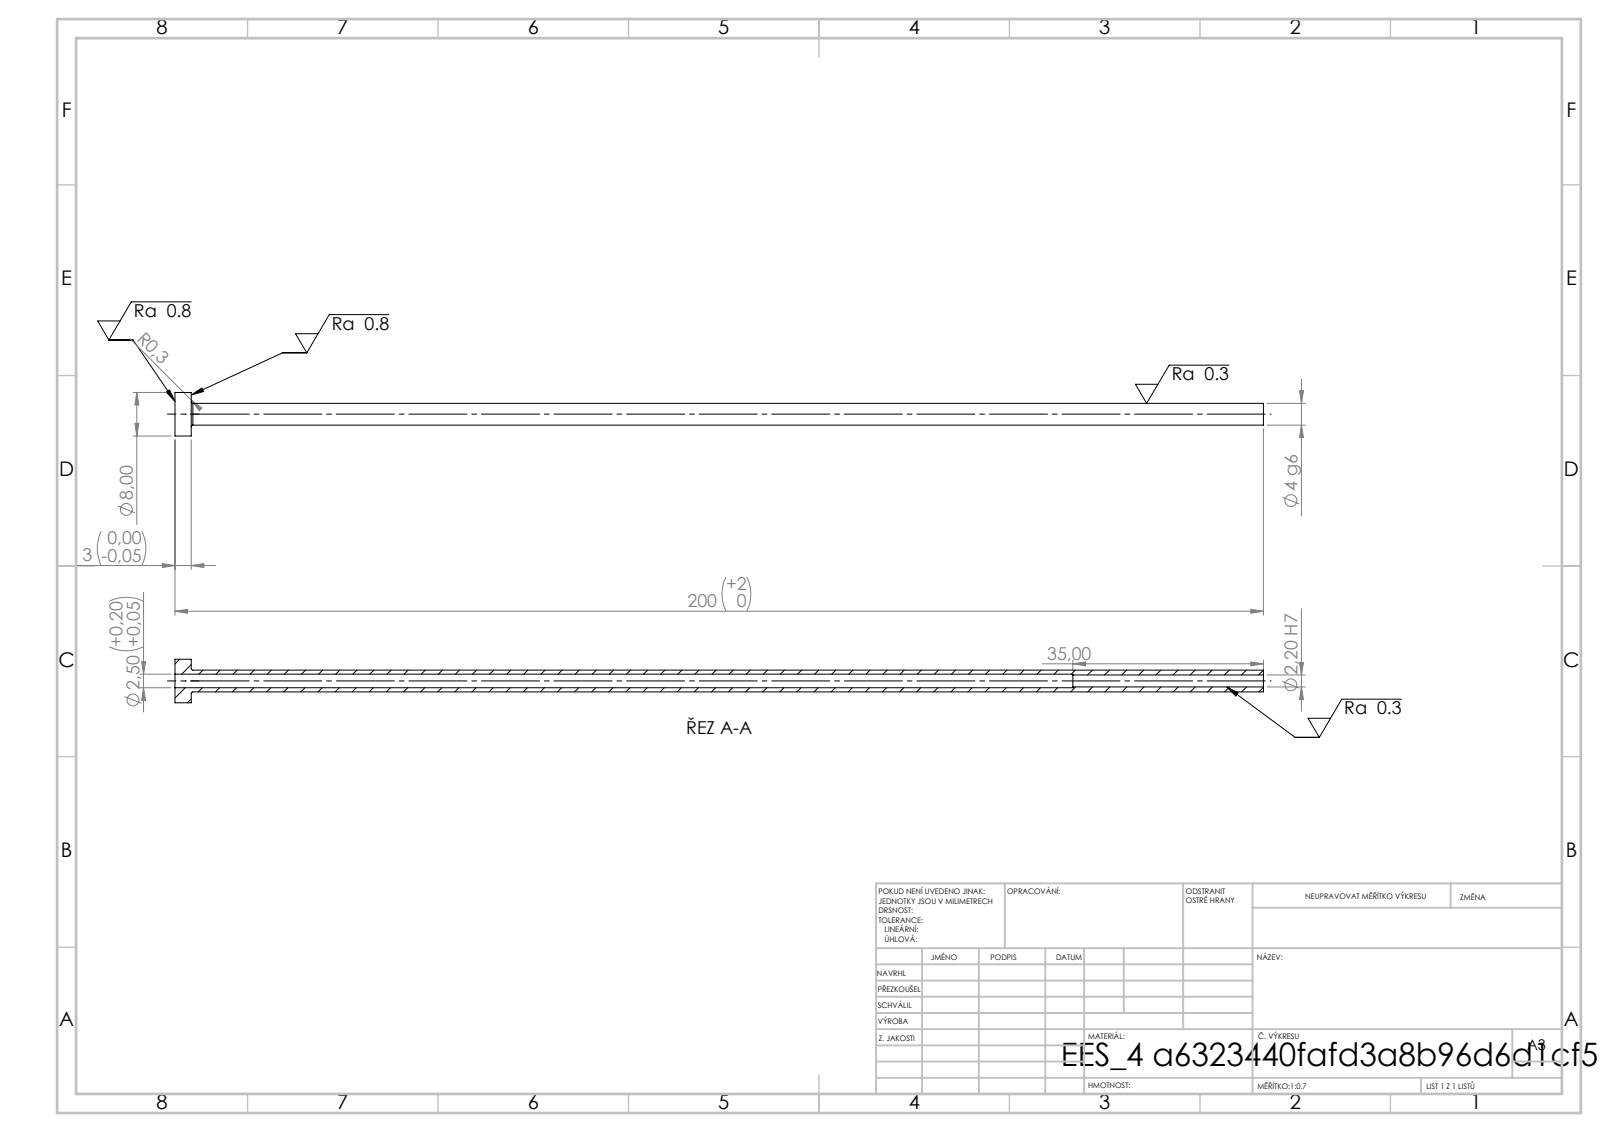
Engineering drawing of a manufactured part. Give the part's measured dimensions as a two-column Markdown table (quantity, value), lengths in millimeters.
| quantity | value |
| --- | --- |
| STEP written by | SolidWorks 2019 (CONFIG_CONTROL_DESIGN) |
| units | millimeters |
| bodies | 1 solid, 14 faces (4 planar, 8 cylindrical, 2 other) |
| overall size | 200 × 8 × 8 |
| volume | 1 684 mm³ |
| surface area | 4 180 mm² |
| round holes (diameter × count) | 2.2 × 1, 2.5 × 1 |
| round bosses / shafts (diameter × count) | 8 × 1, 4 × 1 |
| main face-to-face distances | 3, 200, 197, 165, 162, 35 |
